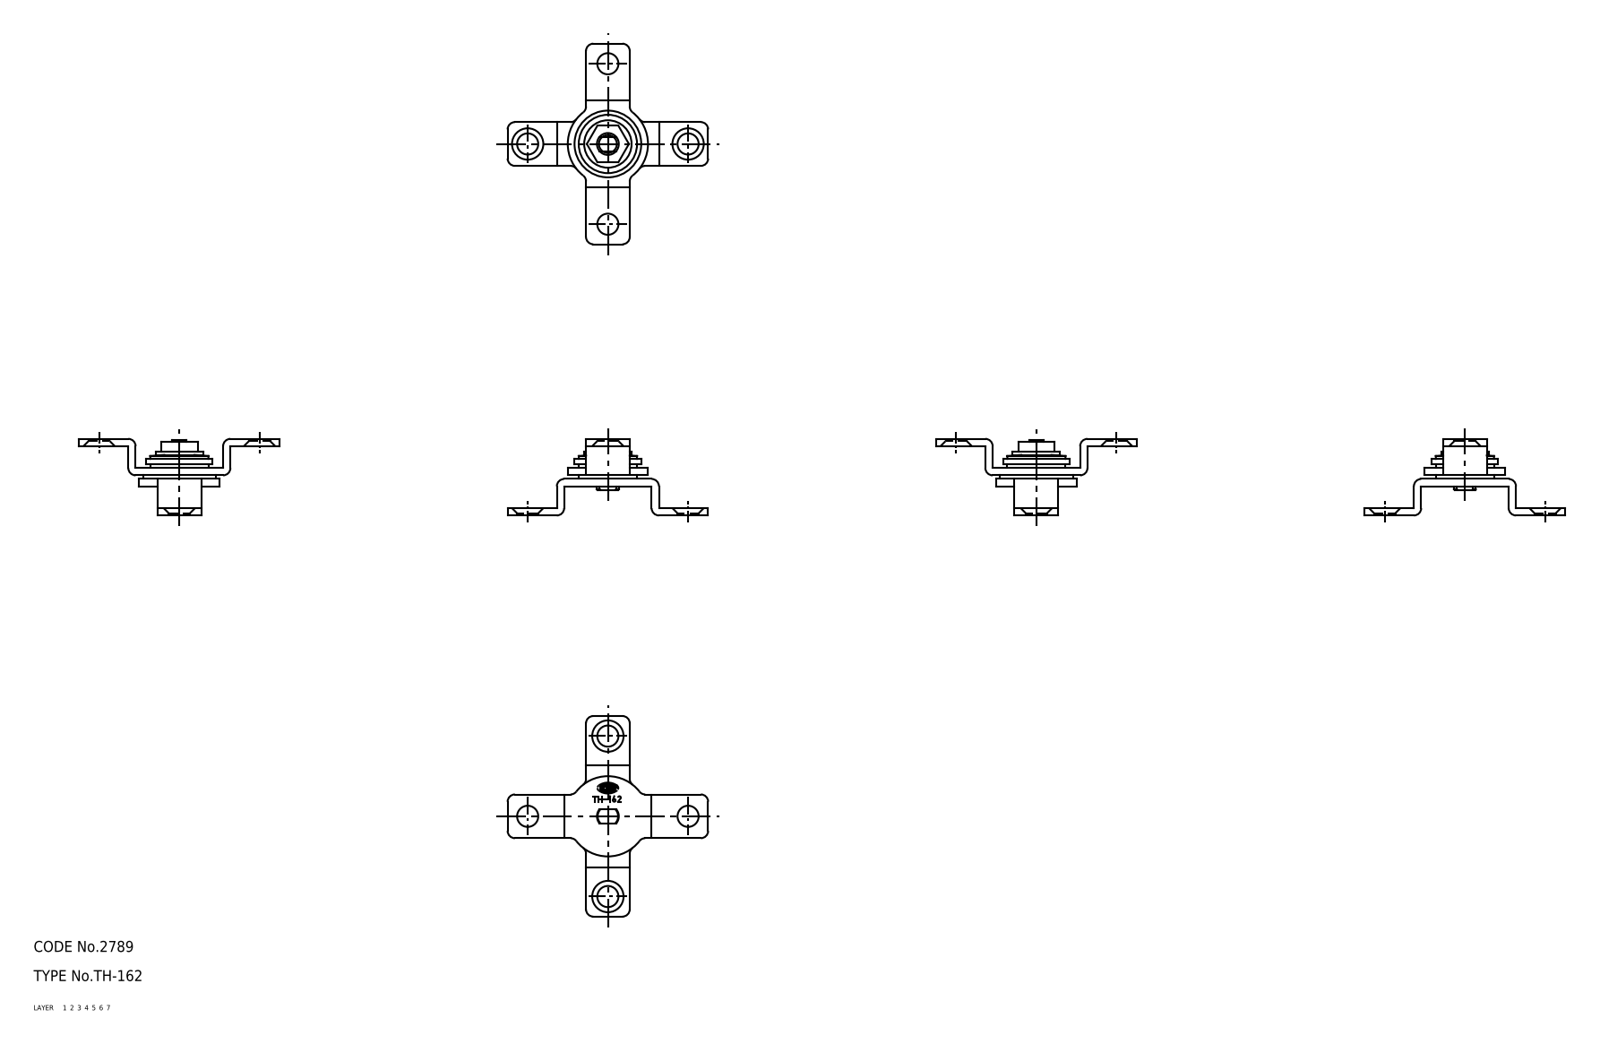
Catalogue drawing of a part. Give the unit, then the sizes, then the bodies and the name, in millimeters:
Units: millimetres
Overall size (bounding box): 55 × 55 × 21
Volume: 4 898 mm³ · Surface area: 5 120 mm²
Bodies: 2 solids, 122 faces (0 planar, 0 cylindrical, 122 other)
Part name (STEP PRODUCT): 67115287; 67115300
STEP written by: CADfix (AUTOMOTIVE_DESIGN)
